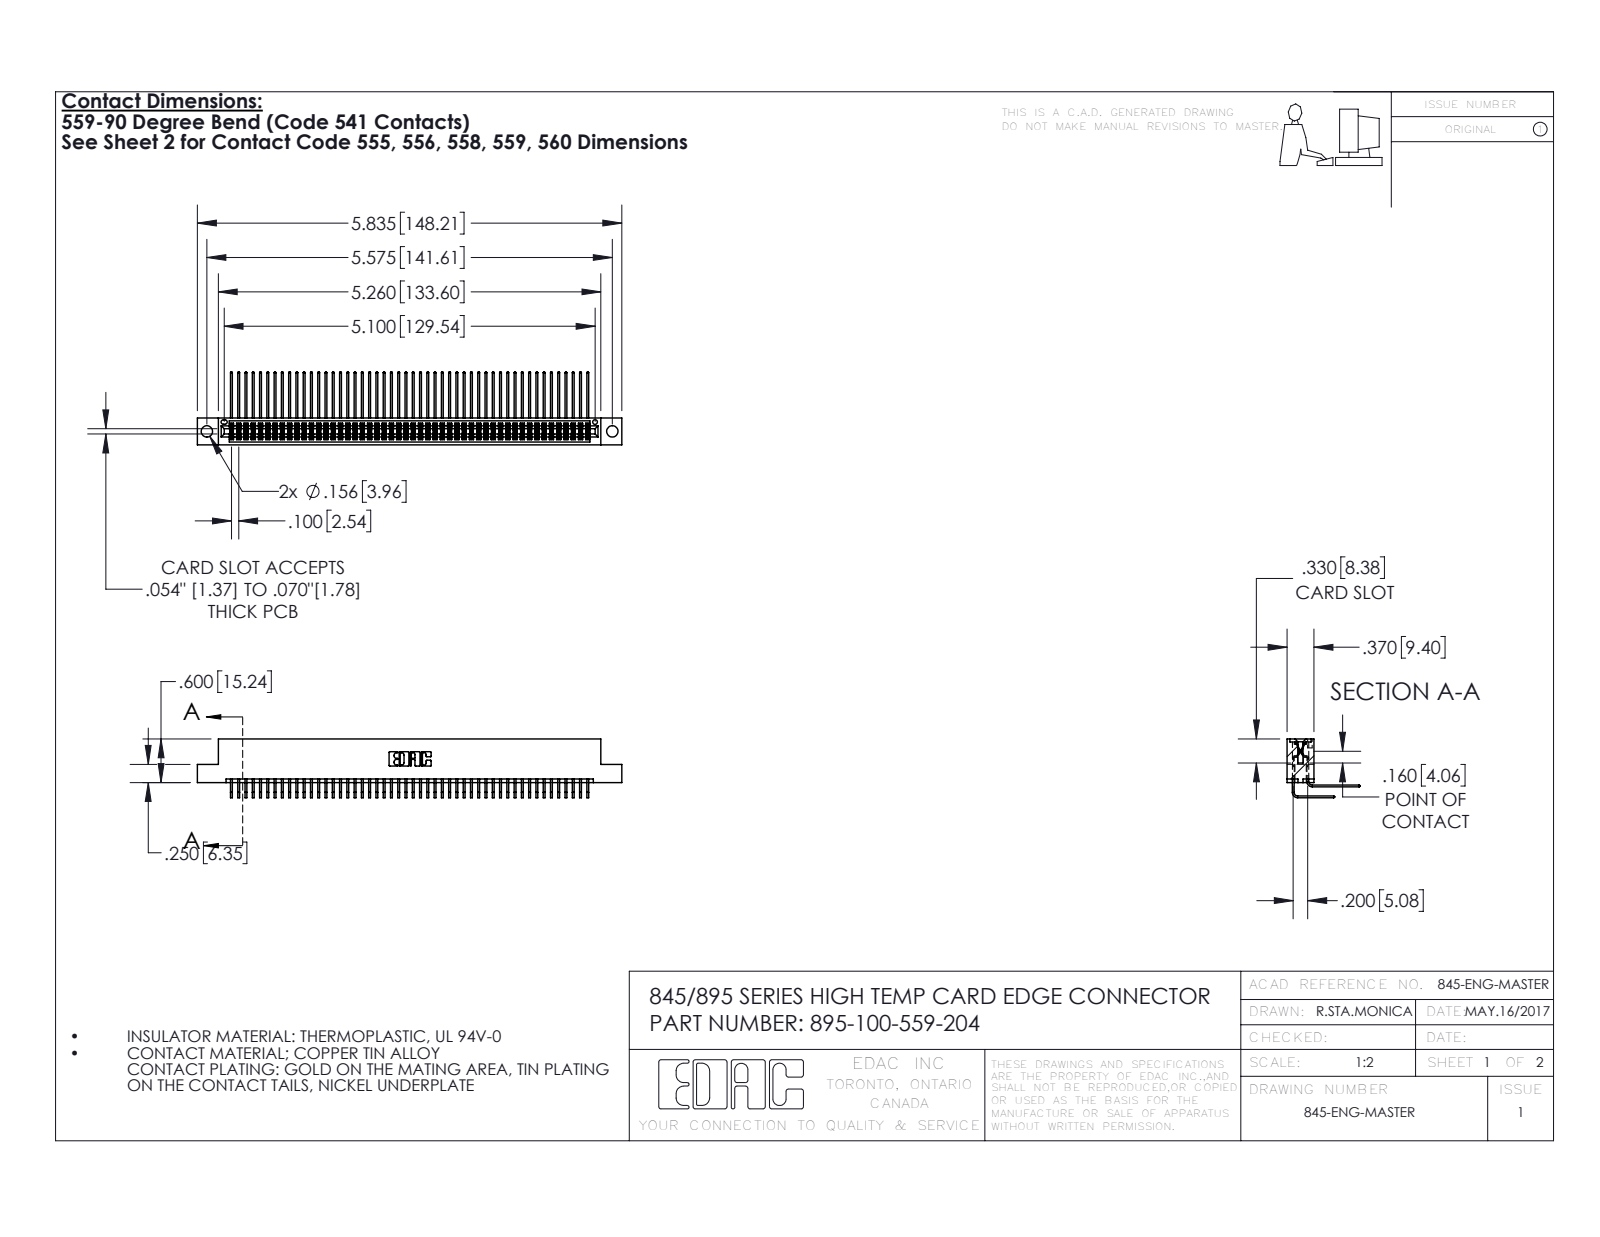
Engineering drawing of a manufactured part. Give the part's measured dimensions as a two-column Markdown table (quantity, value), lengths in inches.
| quantity | value |
| --- | --- |
| part name | 345 Part_Flush Mounting Lugs - 0.156 Dia-TH; 345-292-001_559 Tail - 2; 395-100-559-204; 345-292-001_558 559 Tail - 1 |
| STEP written by | SolidWorks 2016 (CONFIG_CONTROL_DESIGN) |
| units | inches |
| bodies | 101 solids, 5326 faces (3580 planar, 1746 cylindrical, 0 other) |
| overall size | 5.835 × 1.005 × 0.809 |
| volume | 0.913 in³ |
| surface area | 38.44 in² |
| round holes (diameter × count) | 0.156 × 2, 0.064 × 1 |
| partial cylindrical surfaces (radius × count) | 0.006 × 151, 0.01 × 22, 0.007 × 6, 0.031 × 6, 0.026 × 3, 0.014 × 2, 0.019 × 2, 0.022 × 2 |
| main face-to-face distances | 0.072, 0.298, 0.2, 0.37, 0.098, 0.272, 0.025, 0.225, 0.175, 0.15 |
| hole center spacings | 0.27, 5.339, 5.575 |
